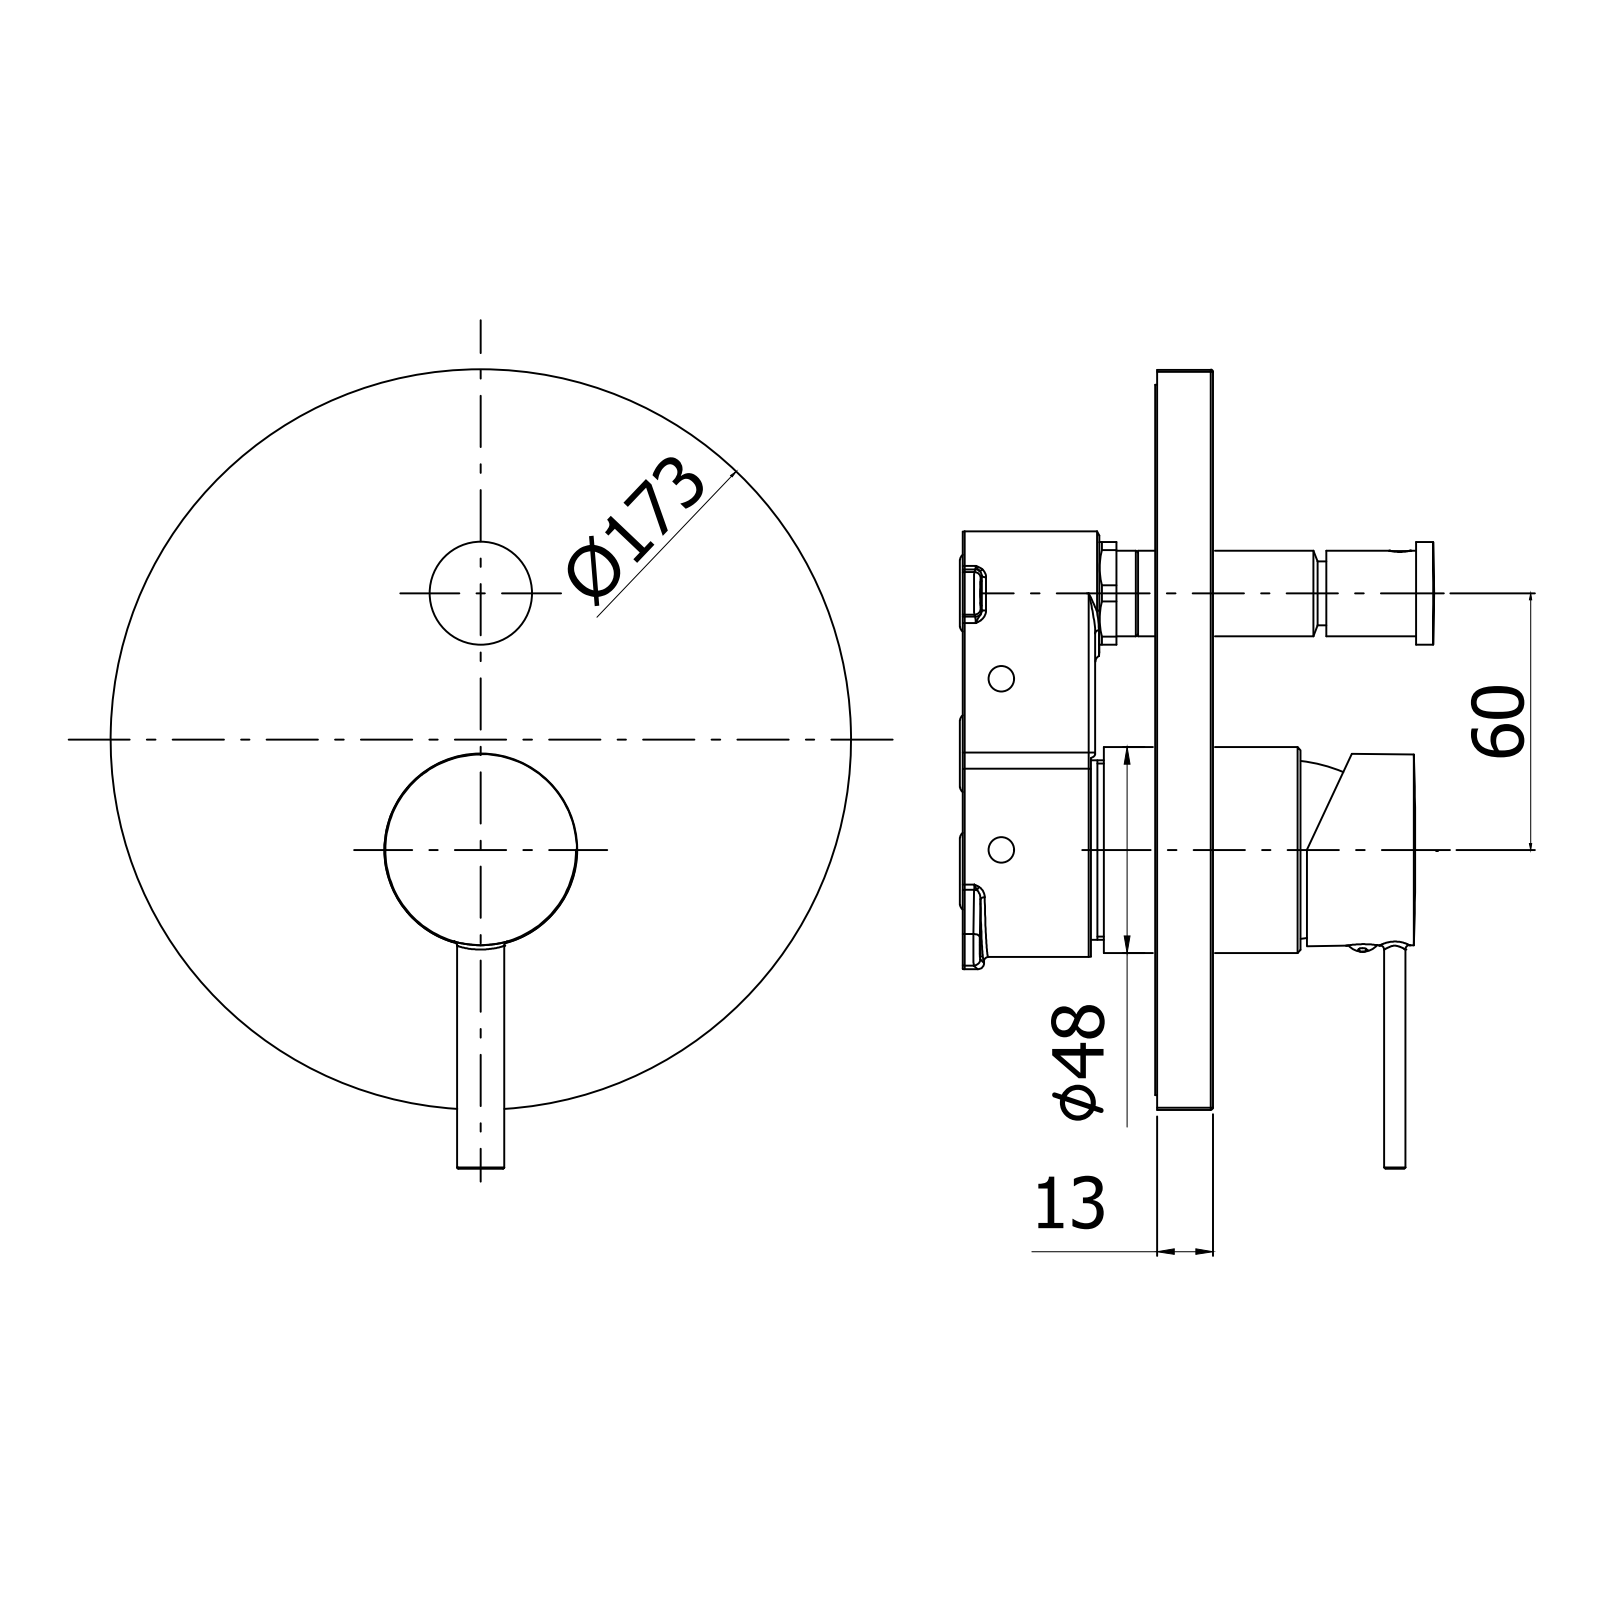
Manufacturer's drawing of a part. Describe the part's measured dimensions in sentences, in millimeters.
The part is named "BRBOX015CR". Its 3-D file was written by "CREO PARAMETRIC BY PTC INC, 2020044 (CONFIG_CONTROL_DESIGN)". It is 5 solids with 1082 faces: 644 planar, 278 cylindrical and 160 other. Overall it measures 186.75 by 173 by 65.21 millimeters. Its volume is 240 551 cubic millimeters and its surface area 120 638 square millimeters. Round holes: 3 of diameter 5, 3 of diameter 7, 2 of diameter 2, 2 of diameter 4, 1 of diameter 3, 1 of diameter 3.3, 1 of diameter 3.5, 1 of diameter 7.1, 1 of diameter 7.8, 1 of diameter 16, 1 of diameter 18.2, 1 of diameter 19.5. Round bosses or shafts: 2 of diameter 4.8, 1 of diameter 173, 1 of diameter 167, 1 of diameter 57, 1 of diameter 48.1, 1 of diameter 39, 1 of diameter 35, 1 of diameter 34.8. Partial cylindrical surfaces (rounded edges, fillets, slot ends): 27 of radius 0.5, 11 of radius 0.15, 4 of radius 0.3, 4 of radius 1, 4 of radius 1.25, 2 of radius 0.8, 2 of radius 2.5, 1 of radius 1.9. The main face-to-face distances are 13, 2, 11, 6.5, 45.5, 58.5, 47.5, 4.5, 10, 52. The hole center spacings are 8.6, 13.45, 15.13, 18.14, 21.93, 31.54, 50.8, 65.38.
